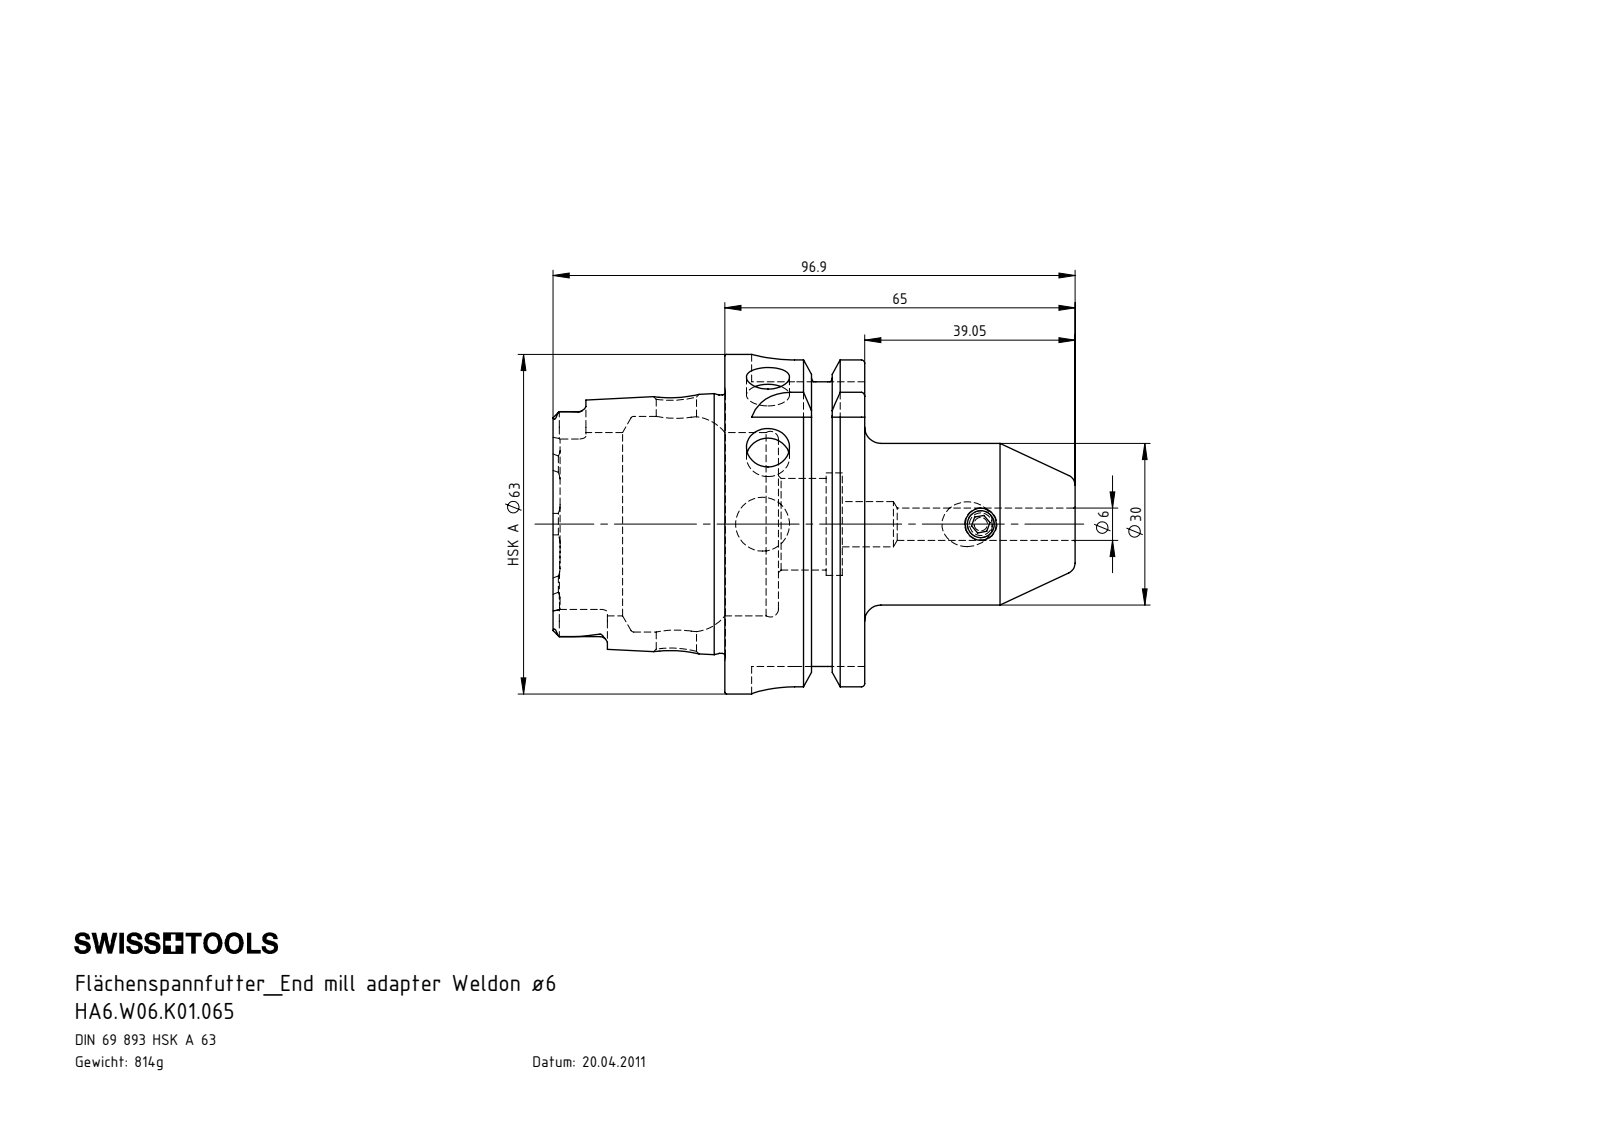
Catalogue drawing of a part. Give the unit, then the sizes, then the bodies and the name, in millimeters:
Units: millimetres
Overall size (bounding box): 96.9 × 63 × 63
Round holes (diameter × count): ⌀8 ×2, ⌀5 ×1, ⌀6 ×1, ⌀7.5 ×1, ⌀8.4 ×1, ⌀10 ×1, ⌀17 ×1, ⌀19 ×1, ⌀34 ×1, ⌀40 ×1
Round bosses / shafts (diameter × count): ⌀63 ×1, ⌀54.95 ×1, ⌀47.94 ×1, ⌀30 ×1, ⌀6 ×1
Partial cylindrical surfaces — rounded edges, fillets, slot ends (radius × count): R1.4 ×6, R2.88 ×4, R8 ×4
Main face-to-face distances: 25.95, 16, 9.95, 31.9, 41.85, 57.85, 52.8, 21.8, 11.85, 53.7
Hole centre spacings: 40.5
Volume: 103 644 mm³ · Surface area: 26 556 mm²
Bodies: 2 solids, 201 faces (57 planar, 55 cylindrical, 89 other)
Part name (STEP PRODUCT): HA6-W06.K01.065; W06-ER1.001.010; HA6-W06.K01.065_B_Fertigbearbeitung
STEP written by: SolidWorks 2012 (AUTOMOTIVE_DESIGN)
